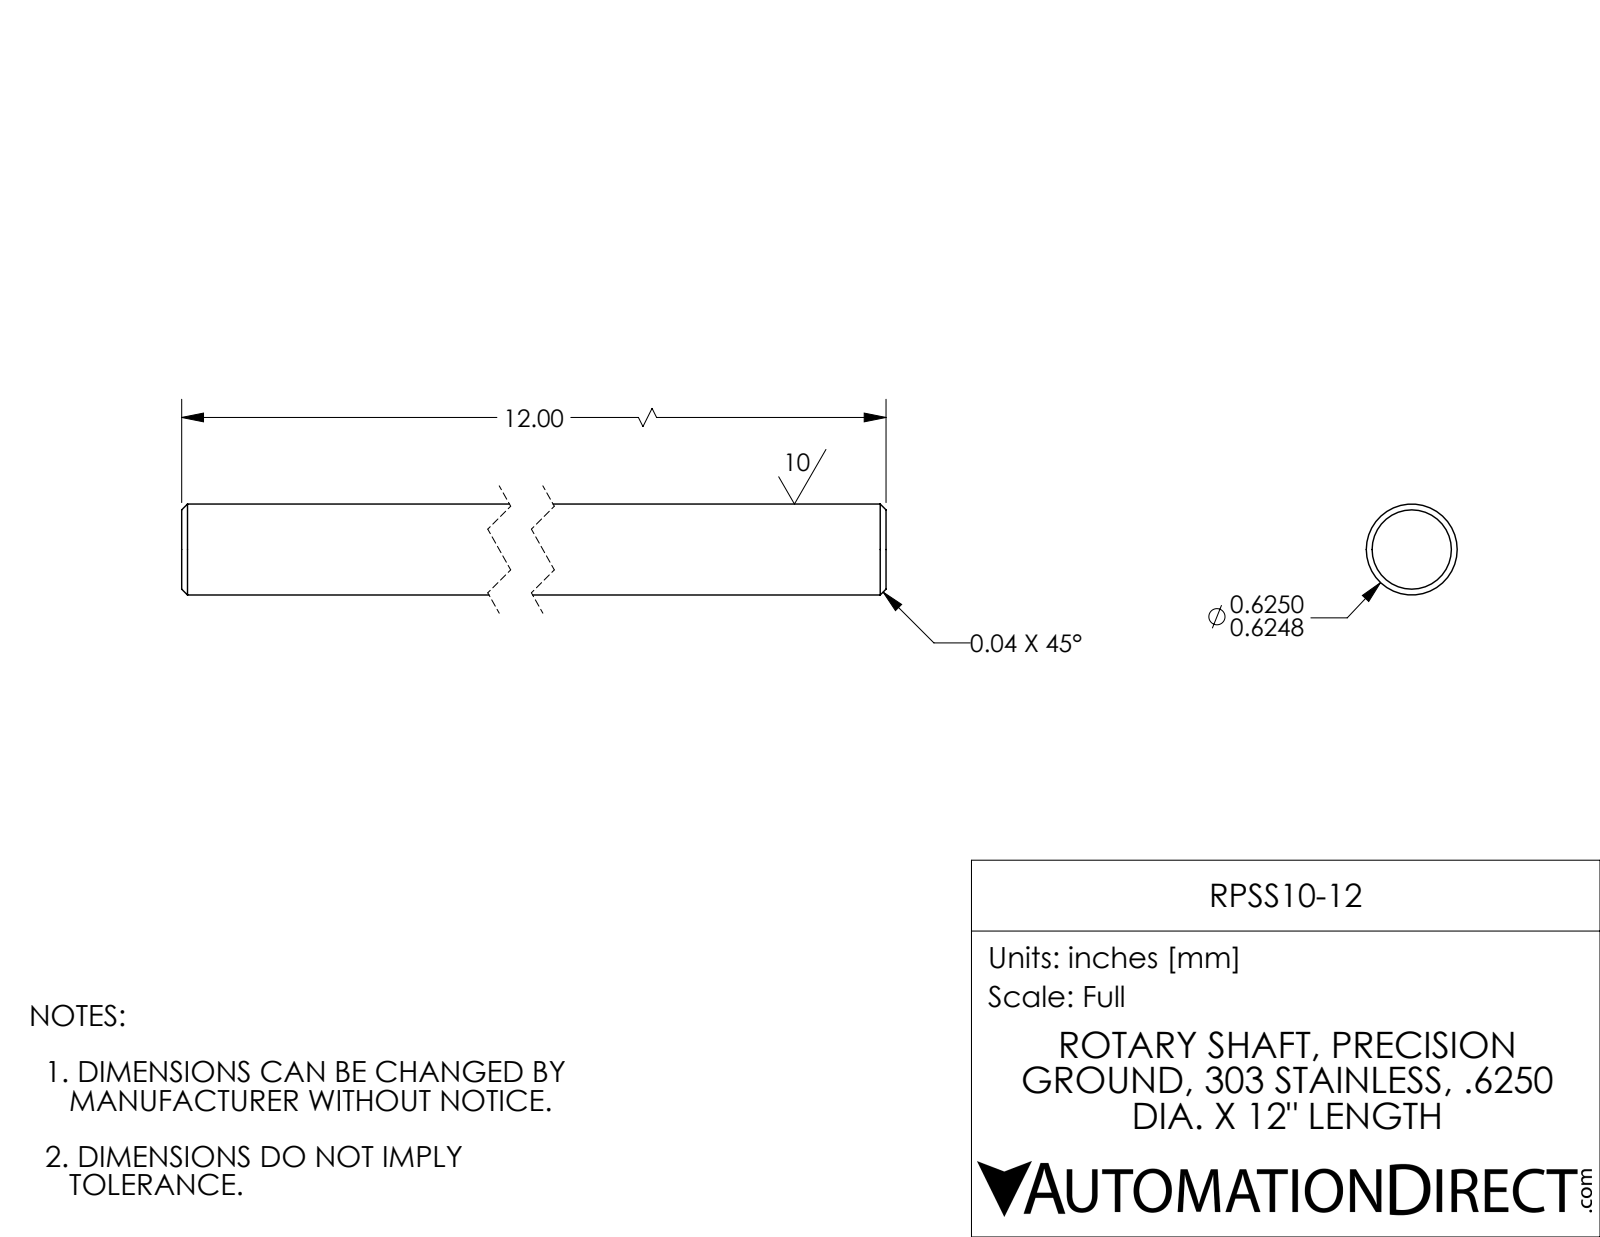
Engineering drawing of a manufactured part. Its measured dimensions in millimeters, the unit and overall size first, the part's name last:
Units: millimetres
Overall size (bounding box): 304.8 × 15.9 × 15.9
Round bosses / shafts (diameter × count): ⌀15.9 ×1
Main face-to-face distances: 304.8
Volume: 60 290 mm³ · Surface area: 15 540 mm²
Bodies: 1 solid, 8 faces (2 planar, 2 cylindrical, 4 other)
Part name (STEP PRODUCT): RPSS10-12
STEP written by: SolidWorks 2017 (AUTOMOTIVE_DESIGN)
